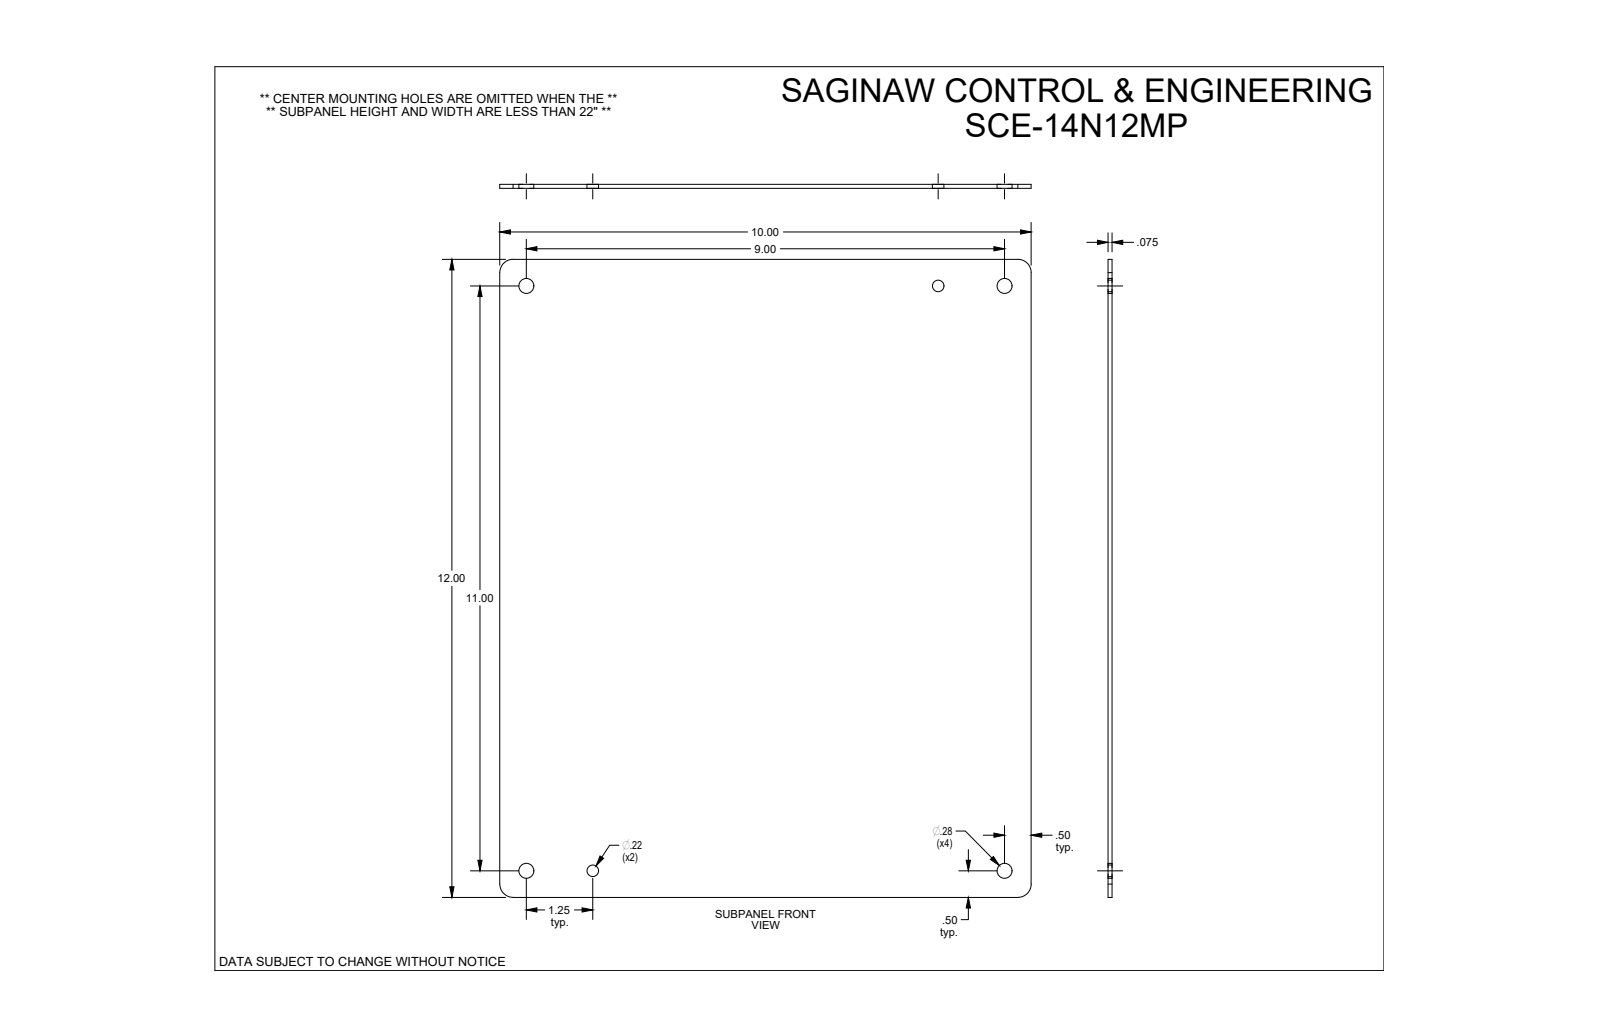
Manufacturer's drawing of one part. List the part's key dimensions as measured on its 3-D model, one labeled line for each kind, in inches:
Part name (STEP PRODUCT): SCE-14N12MP
STEP written by: SolidWorks 2019 (CONFIG_CONTROL_DESIGN)
Units: inches
Bodies: 1 solid, 16 faces (6 planar, 10 cylindrical, 0 other)
Overall size (bounding box): 12 × 10 × 0.075
Volume: 8.972 in³ · Surface area: 242.9 in²
Round holes (diameter × count): ⌀0.281 ×4, ⌀0.218 ×2
Partial cylindrical surfaces — rounded edges, fillets, slot ends (radius × count): R0.25 ×4
Main face-to-face distances: 0.075, 10, 12
Hole centre spacings: 1.25, 7.75, 9, 11, 11.071, 13.456, 14.213, 12.777
